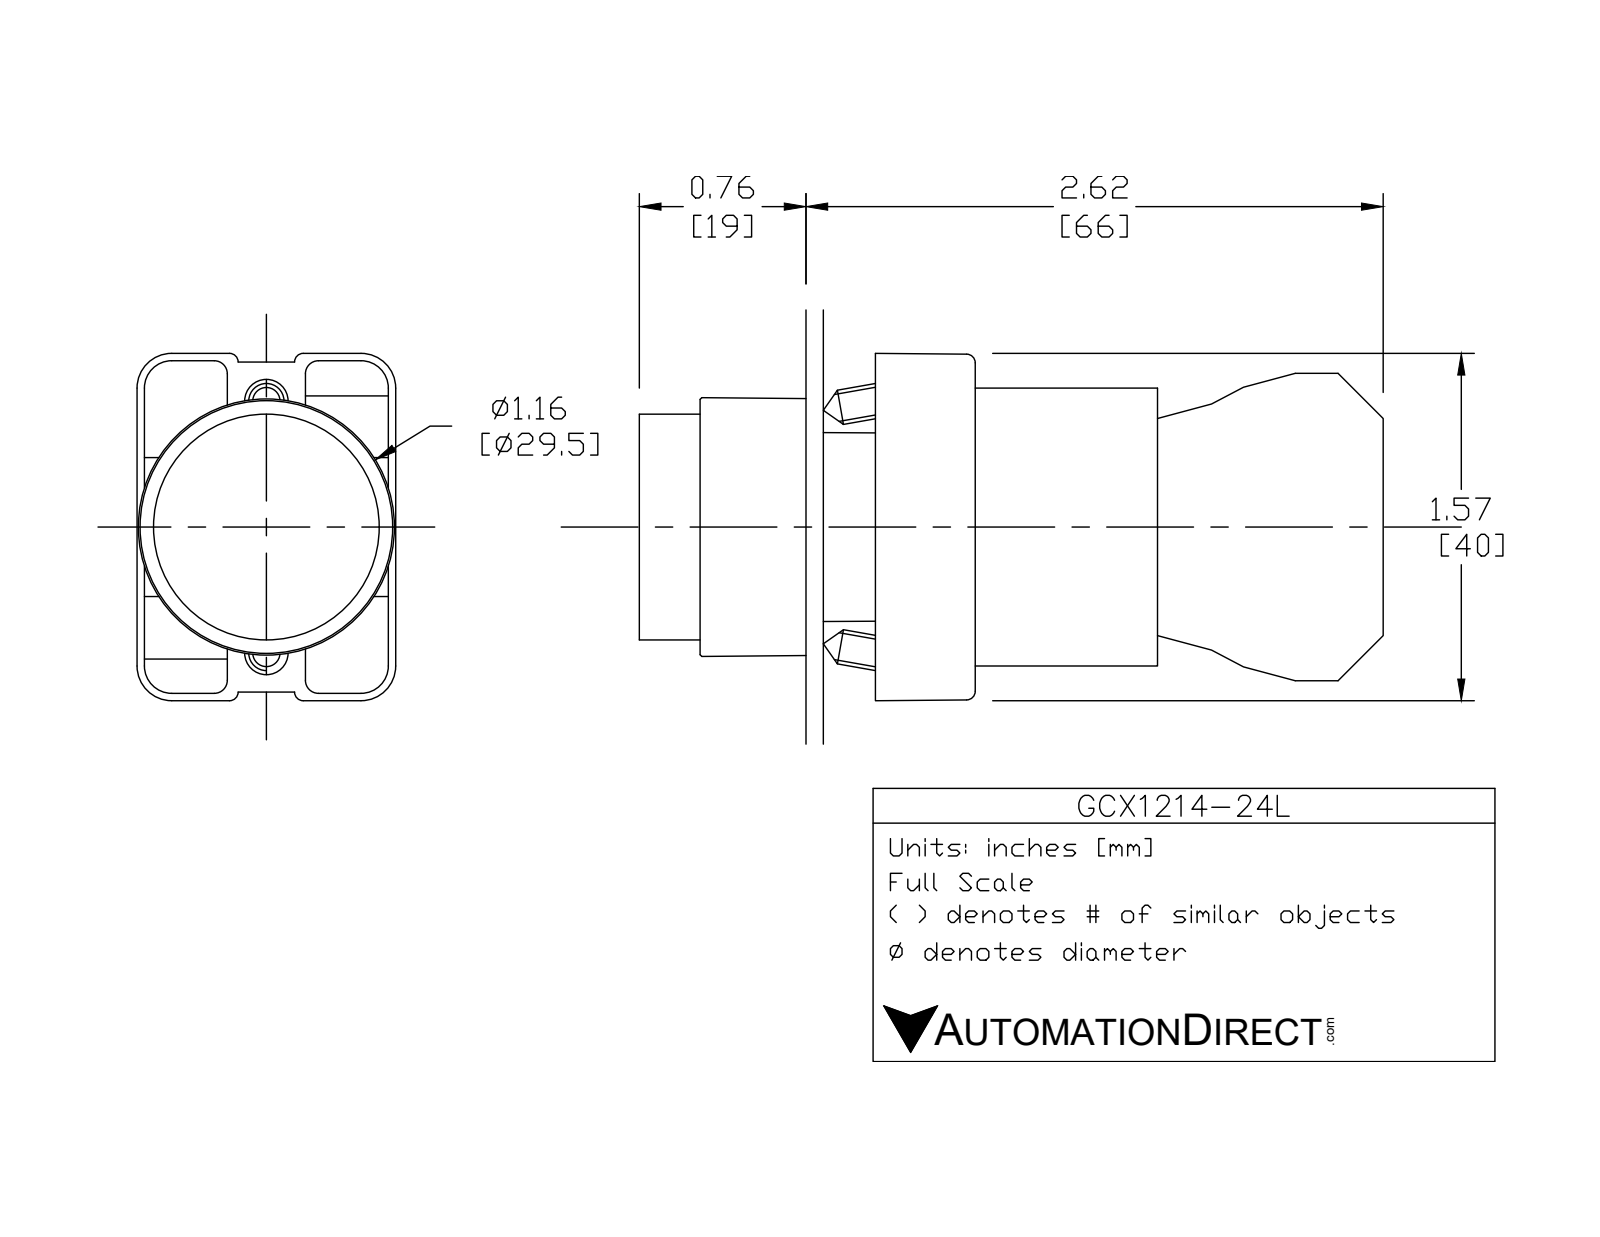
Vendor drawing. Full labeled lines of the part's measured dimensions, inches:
Part name (STEP PRODUCT): GCX1214L OPERATOR; GCX1214-24L; ecx1040; ecx1029 (+1 more)
STEP written by: SolidWorks 2016 (AUTOMOTIVE_DESIGN)
Units: inches
Bodies: 7 solids, 425 faces (250 planar, 144 cylindrical, 31 other)
Overall size (bounding box): 3.319 × 1.581 × 1.177
Volume: 2.721 in³ · Surface area: 36.32 in²
Round holes (diameter × count): ⌀0.079 ×2, ⌀0.124 ×2, ⌀0.13 ×2, ⌀0.087 ×1, ⌀0.197 ×1, ⌀0.469 ×1, ⌀0.878 ×1, ⌀0.888 ×1, ⌀1.024 ×1
Round bosses / shafts (diameter × count): ⌀0.157 ×4, ⌀1.175 ×1, ⌀1.004 ×1, ⌀0.945 ×1, ⌀0.856 ×1, ⌀0.78 ×1, ⌀0.504 ×1
Partial cylindrical surfaces — rounded edges, fillets, slot ends (radius × count): R0.059 ×24, R0.041 ×12, R0.124 ×12, R0.157 ×12, R0.039 ×8, R0.128 ×2, R0.02 ×1, R0.063 ×1
Main face-to-face distances: 0.827, 0.579, 1.171, 2.02, 1.193, 0.031, 0.033, 0.573, 1.165, 0.593
Hole centre spacings: 0.236, 0.544, 0.472, 0.49
